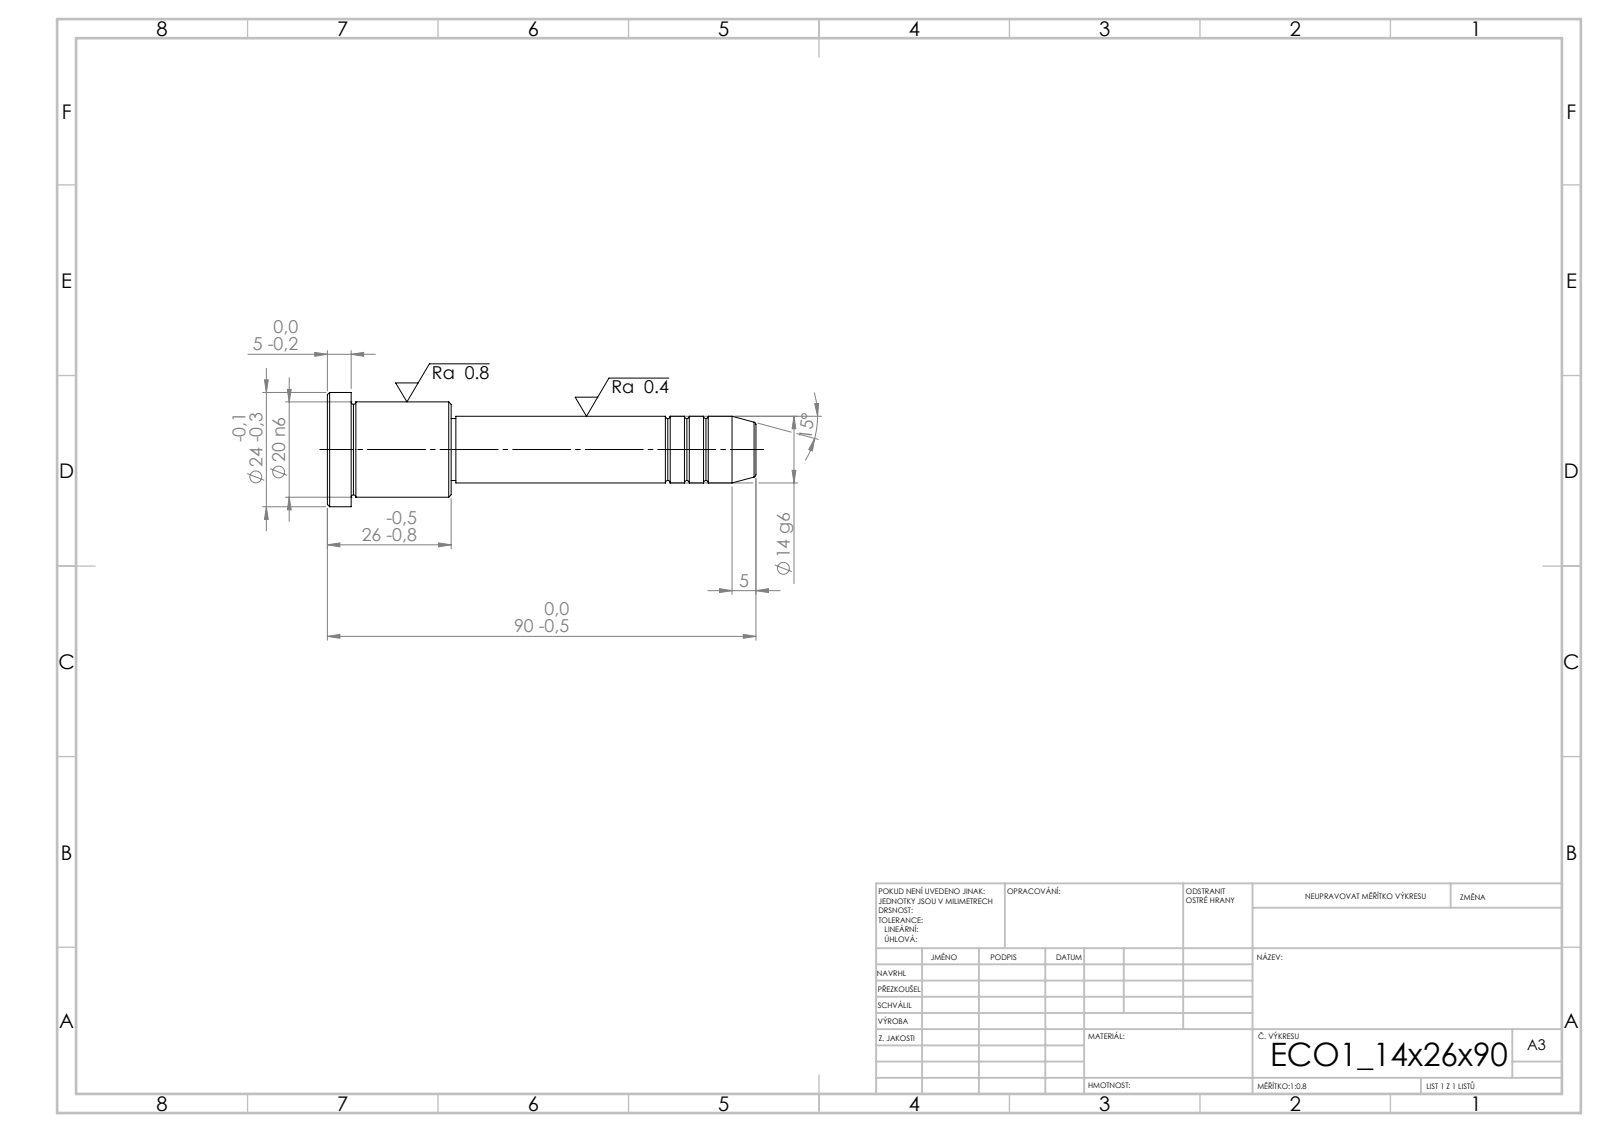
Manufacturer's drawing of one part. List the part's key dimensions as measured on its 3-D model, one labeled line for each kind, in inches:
STEP written by: SolidWorks 2019 (CONFIG_CONTROL_DESIGN)
Units: inches
Bodies: 1 solid, 43 faces (5 planar, 14 cylindrical, 24 other)
Overall size (bounding box): 3.543 × 0.945 × 0.945
Volume: 1.126 in³ · Surface area: 8.434 in²
Round bosses / shafts (diameter × count): ⌀0.945 ×1, ⌀0.787 ×1, ⌀0.551 ×1, ⌀0.512 ×1
Main face-to-face distances: 1.024, 0.827, 0.197, 2.52, 3.346, 3.543, 2.48, 0.039, 0.866, 1.063
